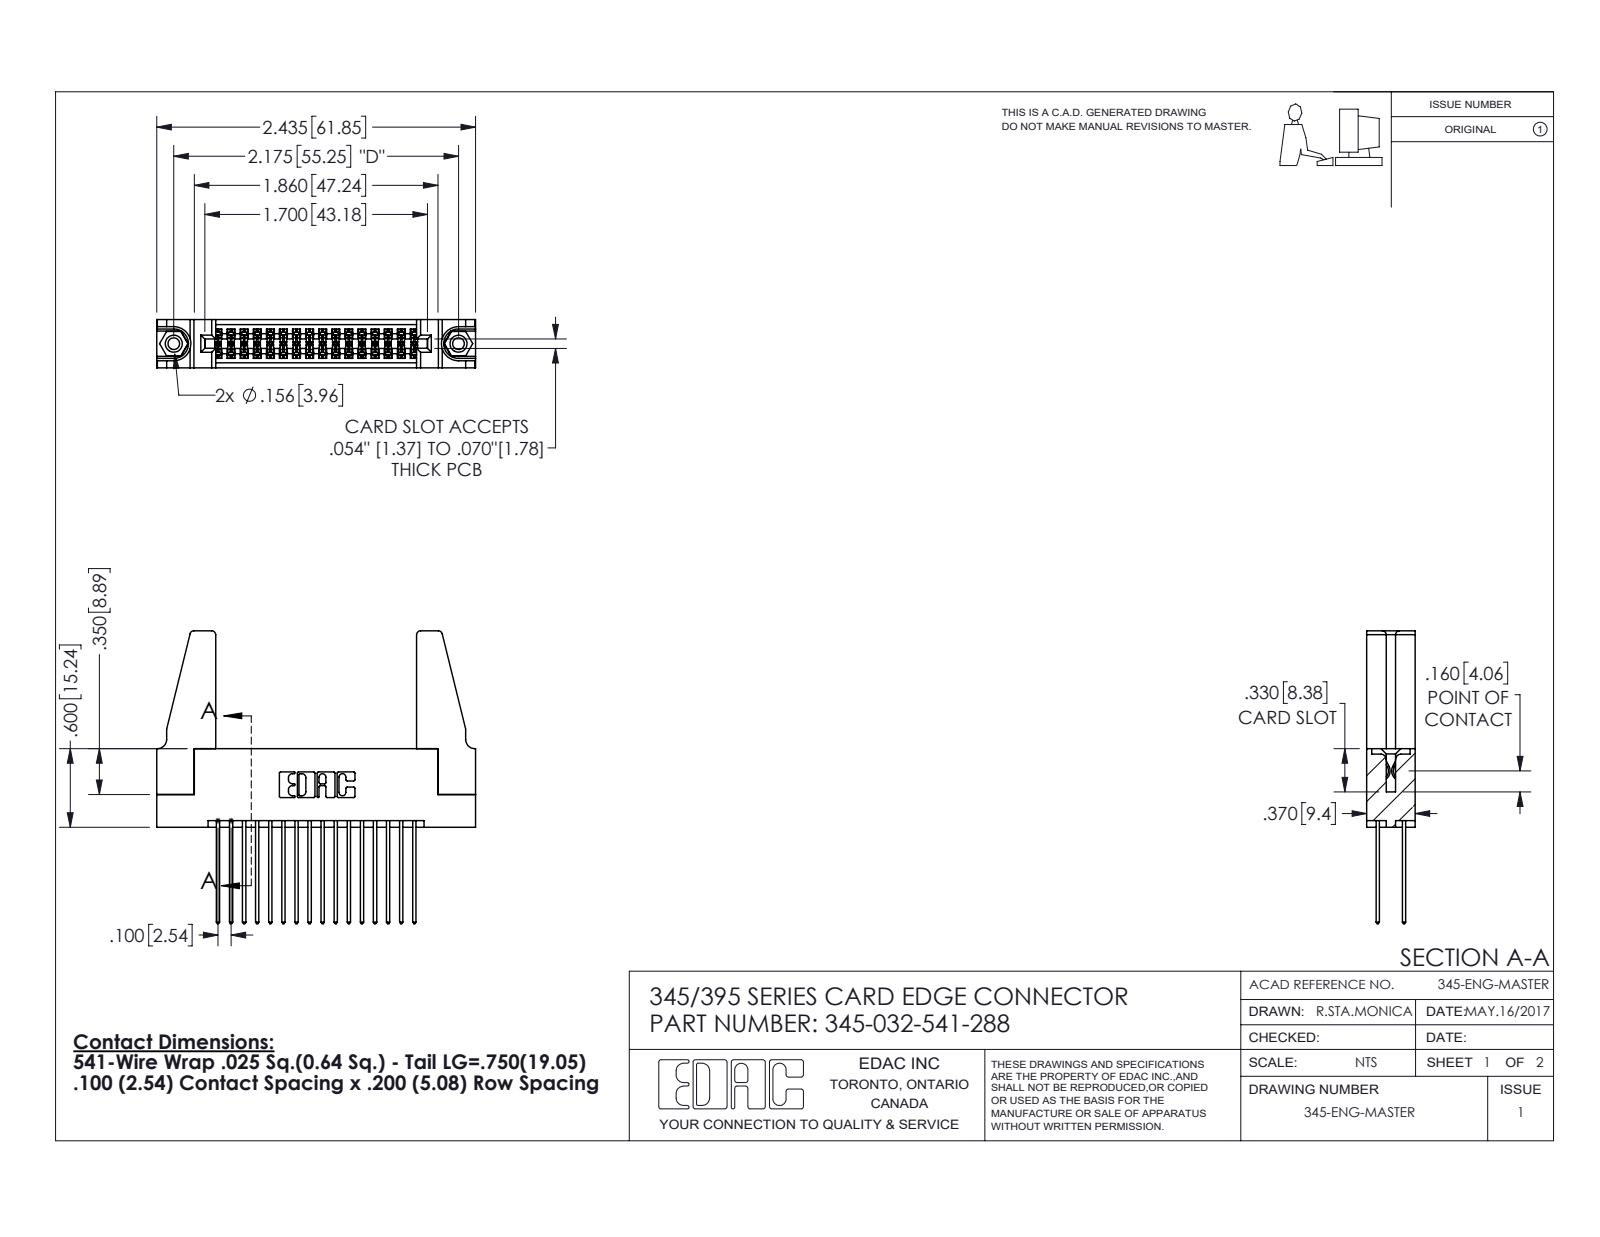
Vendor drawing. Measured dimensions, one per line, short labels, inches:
name: 345-220-078_345-220-088; 345-250-001_345-250-001-102; 345 Part_Flush Mounting Lugs - 0.156 Dia-TH; 345-032-541-288 (+1 more)
written by: SolidWorks 2016 (CONFIG_CONTROL_DESIGN)
unit: in
bodies: 37 solids, 1850 faces (1208 planar, 626 cylindrical, 16 other)
size: 2.436 × 2.237 × 0.37
volume: 0.562 in³; area: 19.04 in²
holes: 2× ⌀0.089, 2× ⌀0.125, 2× ⌀0.156, 1× ⌀0.064
bosses: 2× ⌀0.155
rounds: 48× R0.006, 32× R0.01, 22× R0.01, 8× R0.03, 6× R0.007, 6× R0.031, 3× R0.026, 2× R0.014
face distances: 0.072, 0.298, 0.2, 0.37, 0.098, 0.272, 0.025, 0.225, 0.175, 0.148
hole spacings: 0.27, 1.942, 2.175
